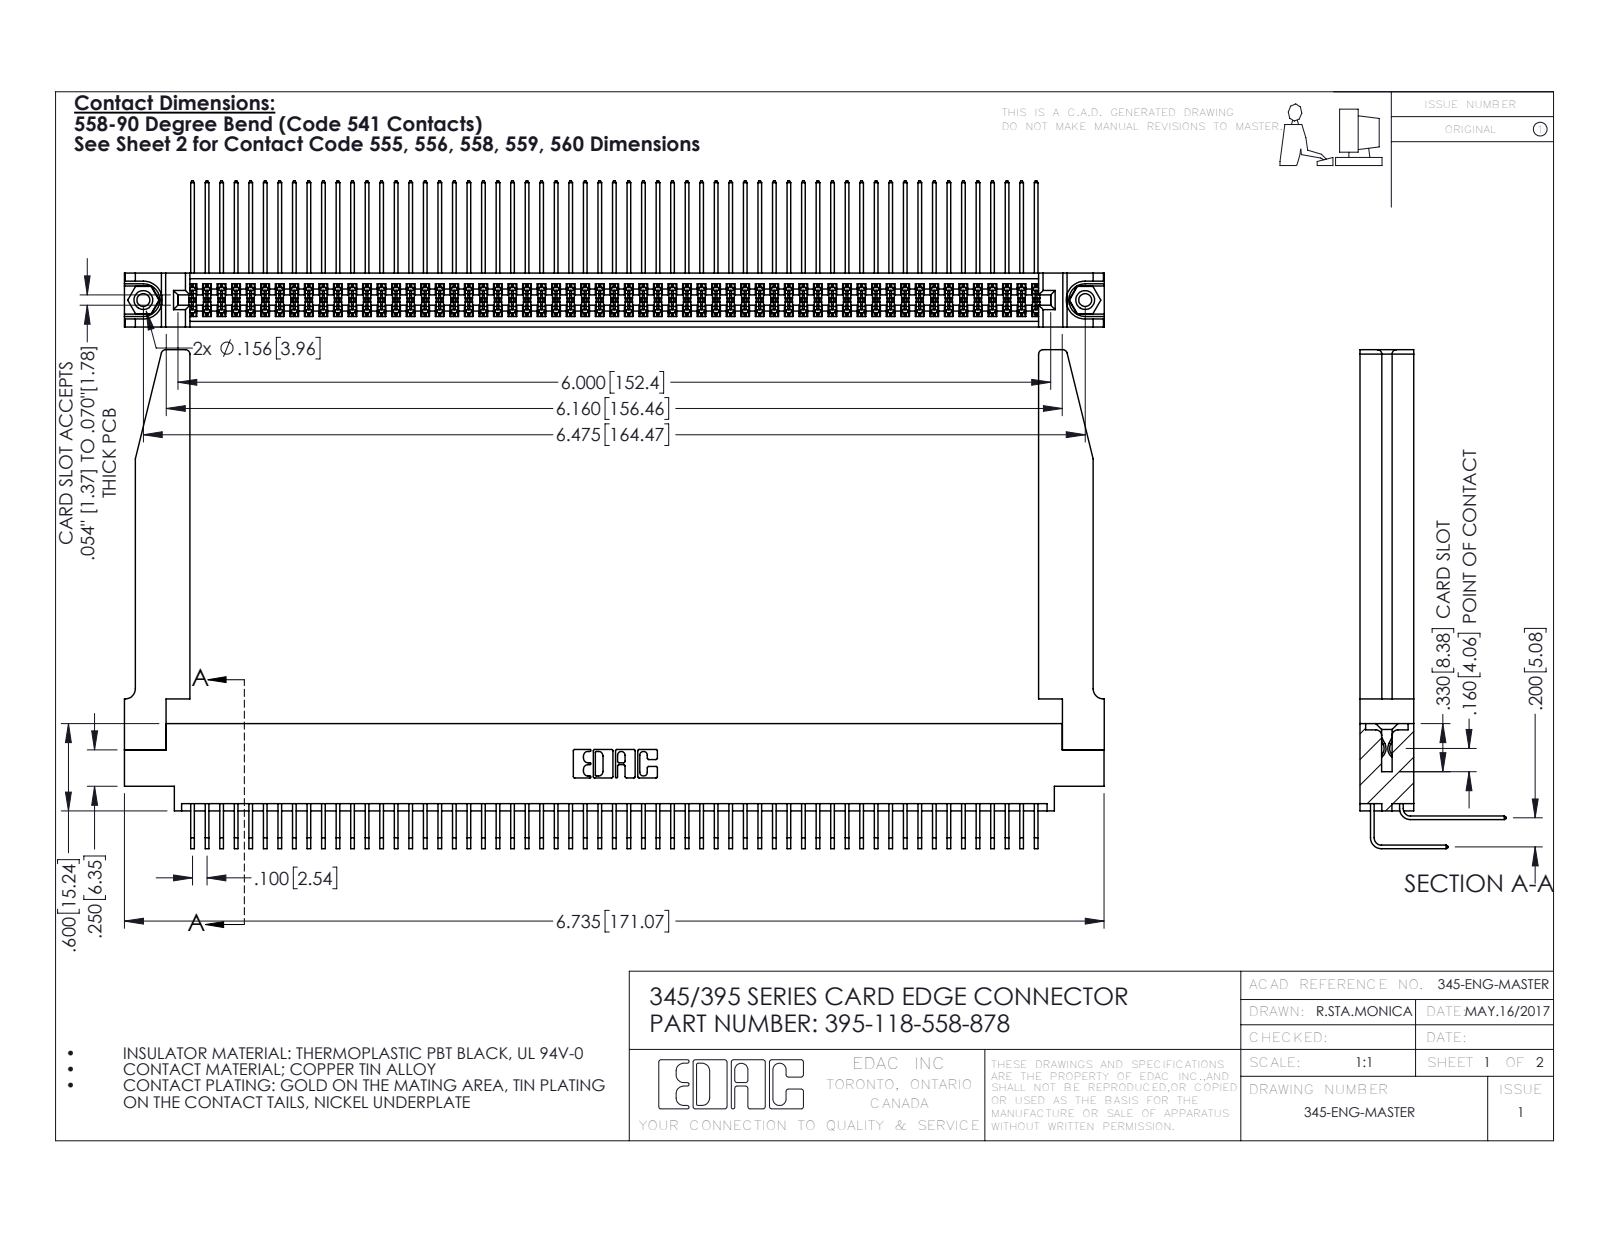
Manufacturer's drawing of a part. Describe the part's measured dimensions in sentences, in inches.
The part is named "345-250-001_345-250-001-102; 345-292-001_558 559 Tail - 1; 345-292-001_558 Tail - 2; 345-220-078_345-220-078 (+2 more)". Its 3-D file was written by "SolidWorks 2016 (CONFIG_CONTROL_DESIGN)". It is 123 solids with 6500 faces: 4356 planar, 2092 cylindrical and 52 other. Overall it measures 6.736 by 3.429 by 1.005 inches. Its volume is 1.533 cubic inches and its surface area 56.03 square inches. Round holes: 2 of diameter 0.089, 2 of diameter 0.125, 2 of diameter 0.156, 1 of diameter 0.064. Round bosses or shafts: 2 of diameter 0.155. Partial cylindrical surfaces (rounded edges, fillets, slot ends): 178 of radius 0.006, 22 of radius 0.01, 8 of radius 0.03, 6 of radius 0.007, 6 of radius 0.031, 3 of radius 0.026, 2 of radius 0.014, 2 of radius 0.019. The main face-to-face distances are 0.072, 0.298, 0.37, 0.2, 0.098, 0.272, 0.025, 0.225, 0.175, 0.025. The hole center spacings are 0.27, 6.239, 6.475.
